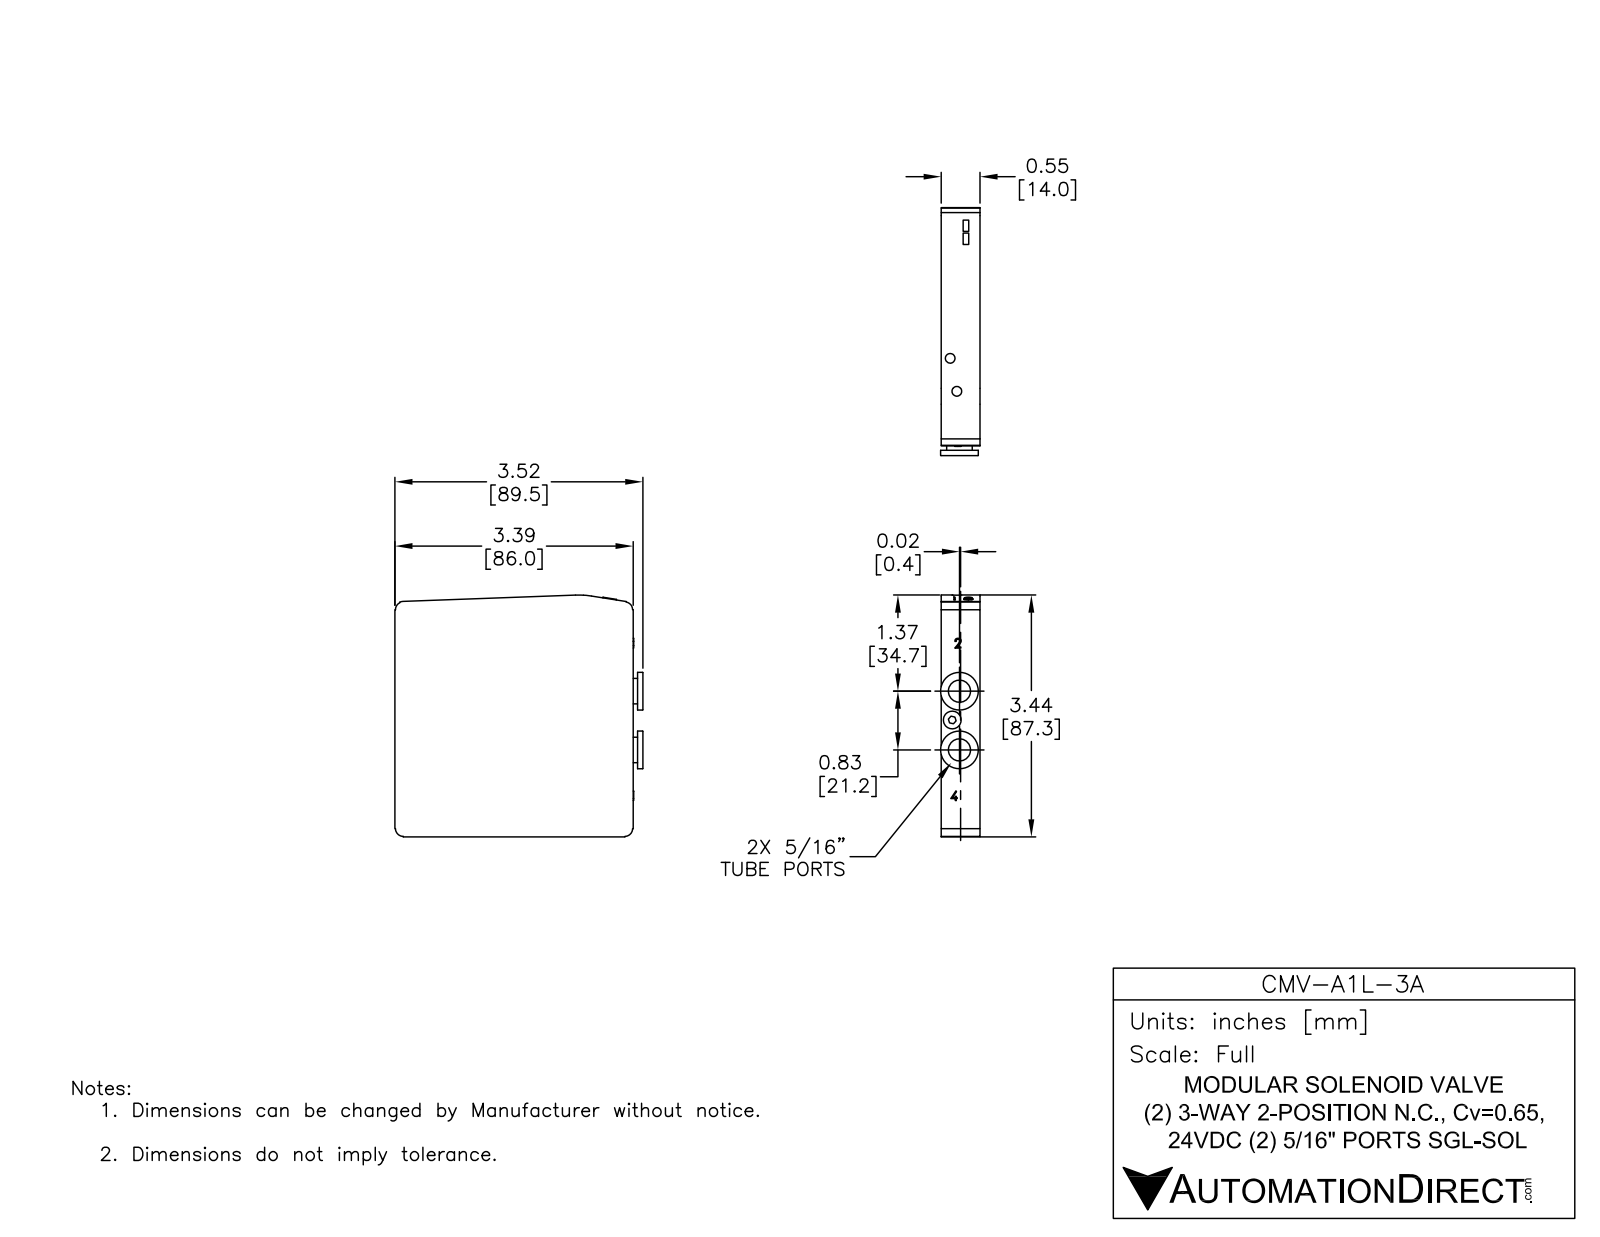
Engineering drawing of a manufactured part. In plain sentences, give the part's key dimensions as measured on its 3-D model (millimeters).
The part is named "CMV-A1L-3A". Its 3-D file was written by "SolidWorks 2013 (AUTOMOTIVE_DESIGN)". It is 78 solids with 1140 faces: 879 planar, 162 cylindrical and 99 other. Overall it measures 89.5 by 87.3 by 22.93 millimeters. Its volume is 95 435 cubic millimeters and its surface area 47 240 square millimeters. Round holes: 4 of diameter 5.25, 2 of diameter 3.35, 2 of diameter 4.4, 2 of diameter 6.5, 2 of diameter 8, 2 of diameter 9.8, 2 of diameter 11.5, 1 of diameter 3.6, 1 of diameter 4.5, 1 of diameter 6.25, 1 of diameter 6.4. Round bosses or shafts: 4 of diameter 1.5, 2 of diameter 13.6, 2 of diameter 9.2, 2 of diameter 6.25, 2 of diameter 5.75, 2 of diameter 4.2, 2 of diameter 4, 1 of diameter 3.5. Partial cylindrical surfaces (rounded edges, fillets, slot ends): 12 of radius 2.35, 4 of radius 0.78, 4 of radius 1.5, 4 of radius 2.8, 2 of radius 1, 1 of radius 0.15, 1 of radius 0.17, 1 of radius 0.25. The main face-to-face distances are 14, 4, 10, 3, 1, 83, 5, 15, 29.75, 14.33. The hole center spacings are 9.7, 20.2, 22.17, 8.67, 8.68, 8.82, 9.6, 10.61.
